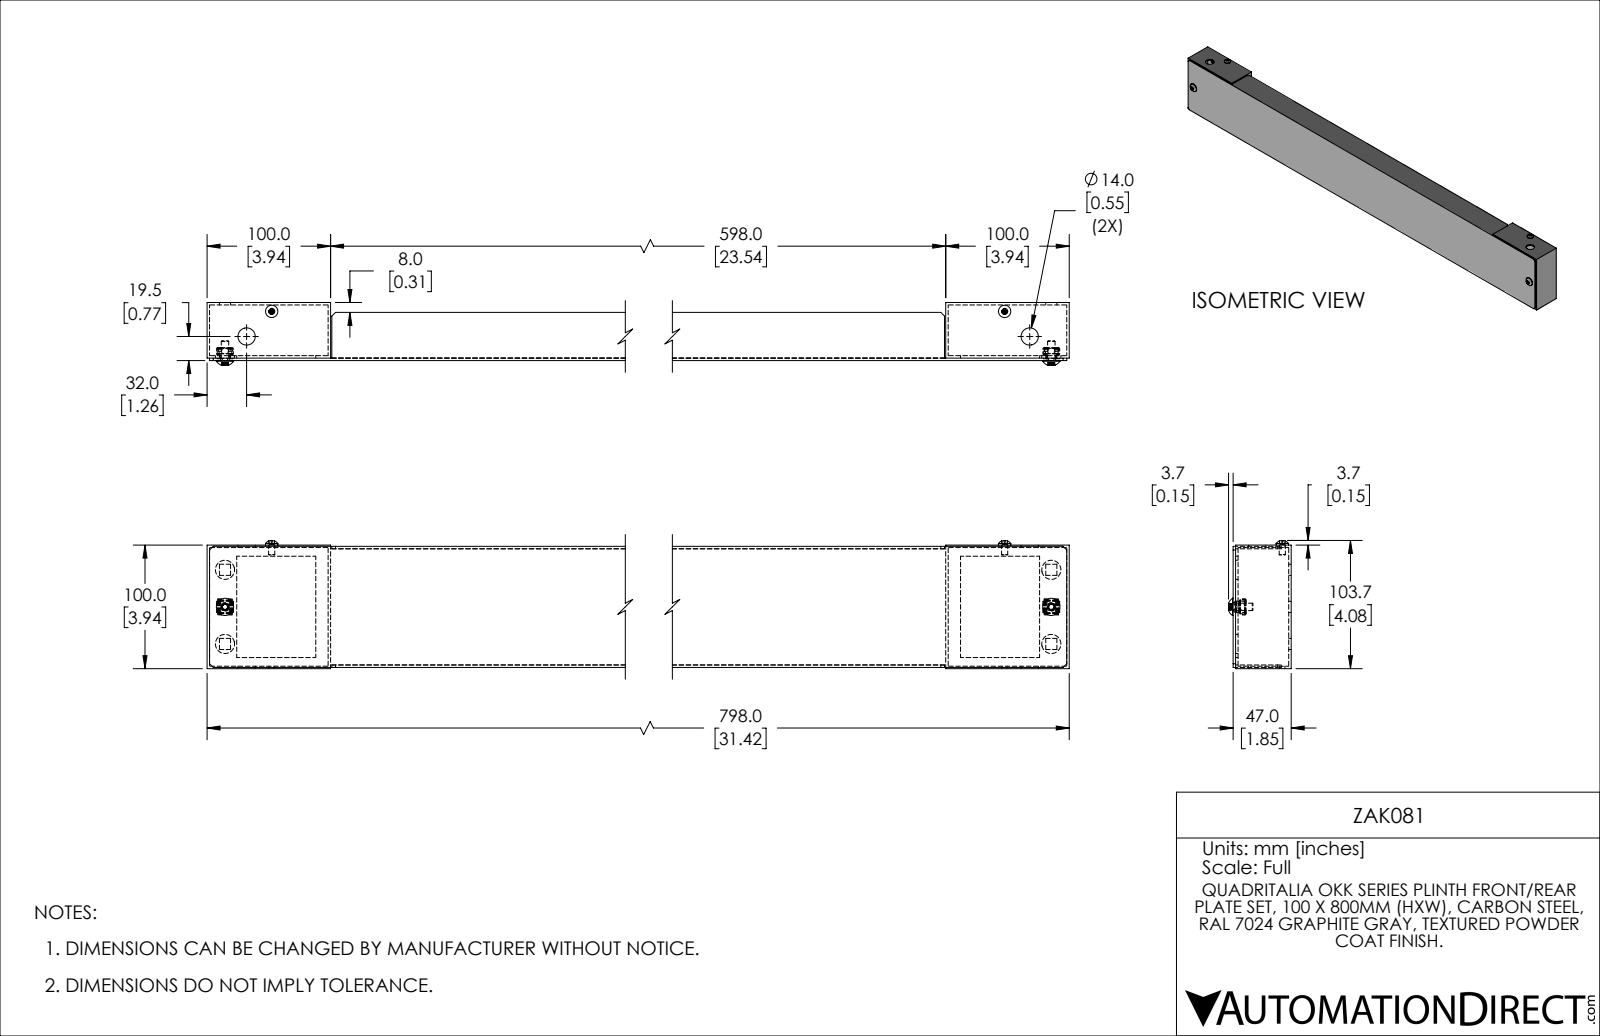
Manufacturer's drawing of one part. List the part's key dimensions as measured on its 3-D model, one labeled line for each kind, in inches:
Part name (STEP PRODUCT): ZAK081
STEP written by: SolidWorks 2021 (CONFIG_CONTROL_DESIGN)
Units: inches
Bodies: 11 solids, 400 faces (250 planar, 132 cylindrical, 18 other)
Overall size (bounding box): 31.417 × 4.084 × 1.996
Volume: 22.35 in³ · Surface area: 579.7 in²
Round holes (diameter × count): ⌀0.61 ×4, ⌀0.167 ×2, ⌀0.194 ×2, ⌀0.276 ×2, ⌀0.551 ×2
Round bosses / shafts (diameter × count): ⌀0.551 ×2, ⌀0.394 ×2, ⌀0.236 ×2, ⌀0.197 ×2
Partial cylindrical surfaces — rounded edges, fillets, slot ends (radius × count): R0.02 ×42, R0.01 ×28, R0.039 ×18
Main face-to-face distances: 0.079, 3.78, 3.858, 0.039, 1.772, 3.819, 1.693, 3.701, 1.85, 0.118
Hole centre spacings: 1.181, 30.298, 30.276, 1.13, 2.362, 28.11, 30.368, 27.299
